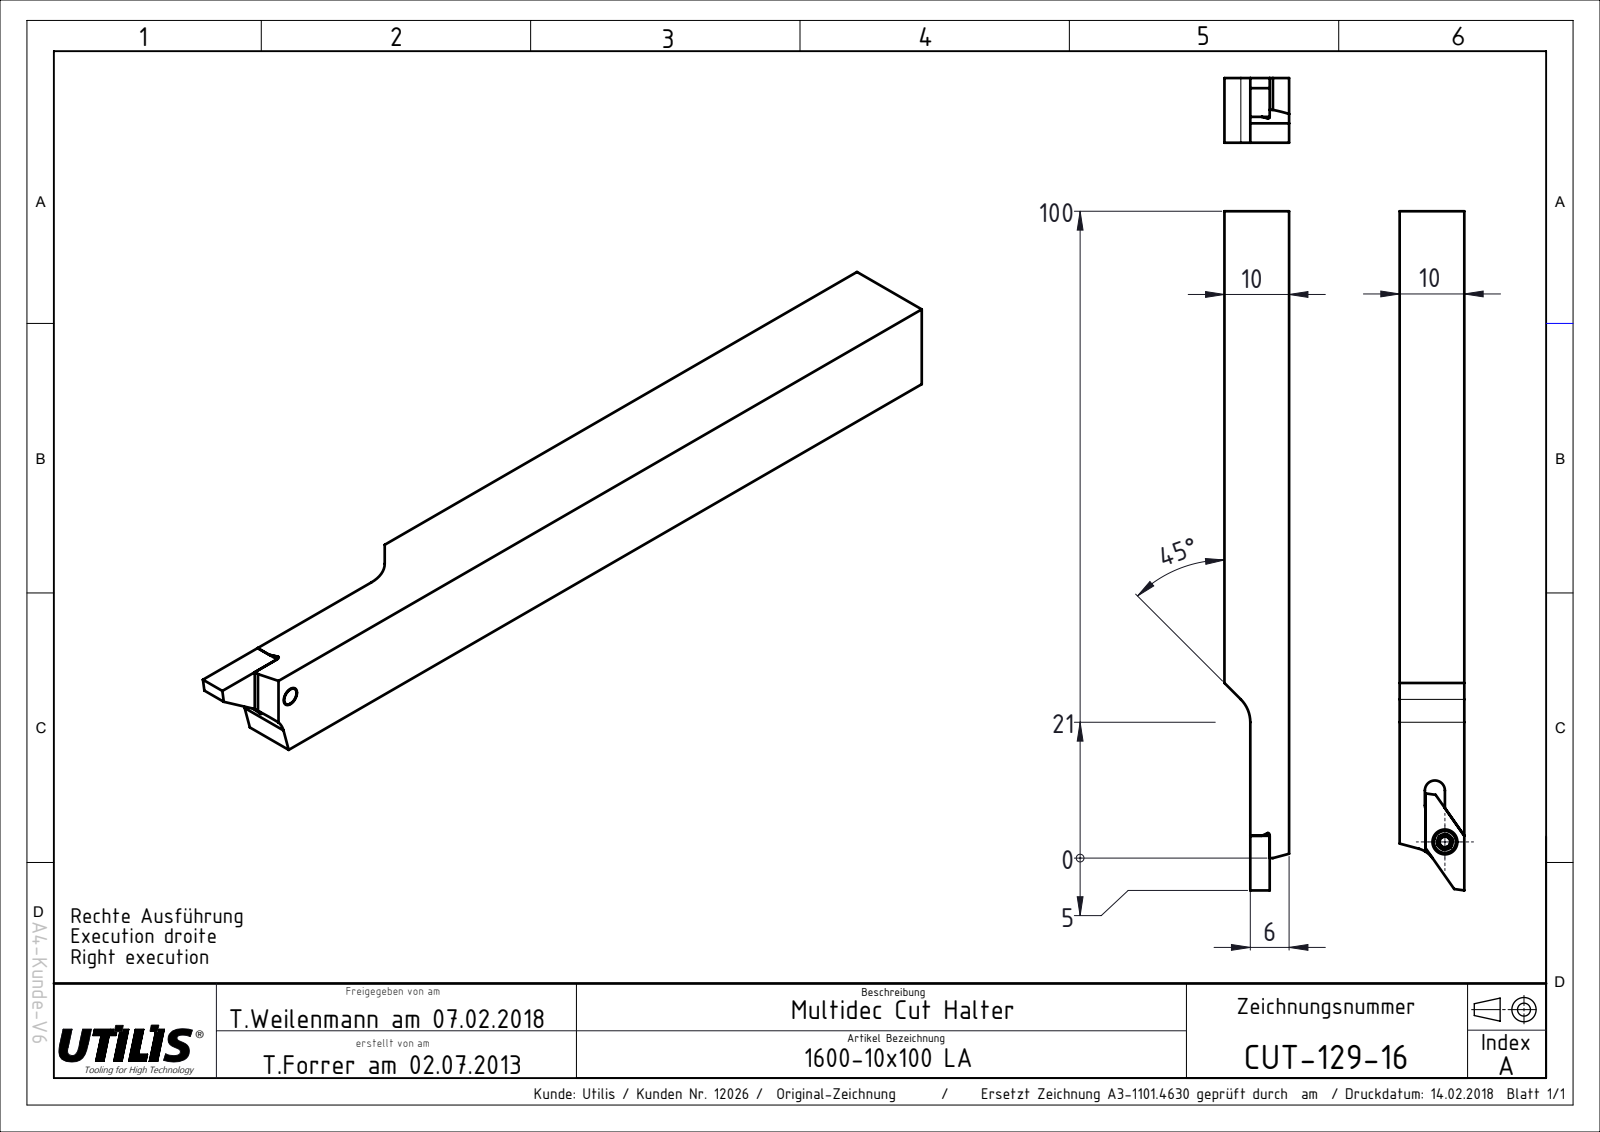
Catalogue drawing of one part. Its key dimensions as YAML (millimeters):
part_name: "CUT-129-16"
step_written_by: "SolidWorks 2017 (AUTOMOTIVE_DESIGN)"
units: millimeters
bodies: {solids: 1, faces: 36, planar: 31, cylindrical: 5, other: 0}
overall_size: [105, 10, 10]
volume: 8978
surface_area: 4054
partial_cylinders:
  - {radius: 1.5, count: 1}
  - {radius: 1.55, count: 1}
  - {radius: 4, count: 1}
  - {radius: 5, count: 1}
face_to_face_distances: [10, 4, 6, 3, 7, 6.01, 3.9, 3.1, 6.1, 14.02]
